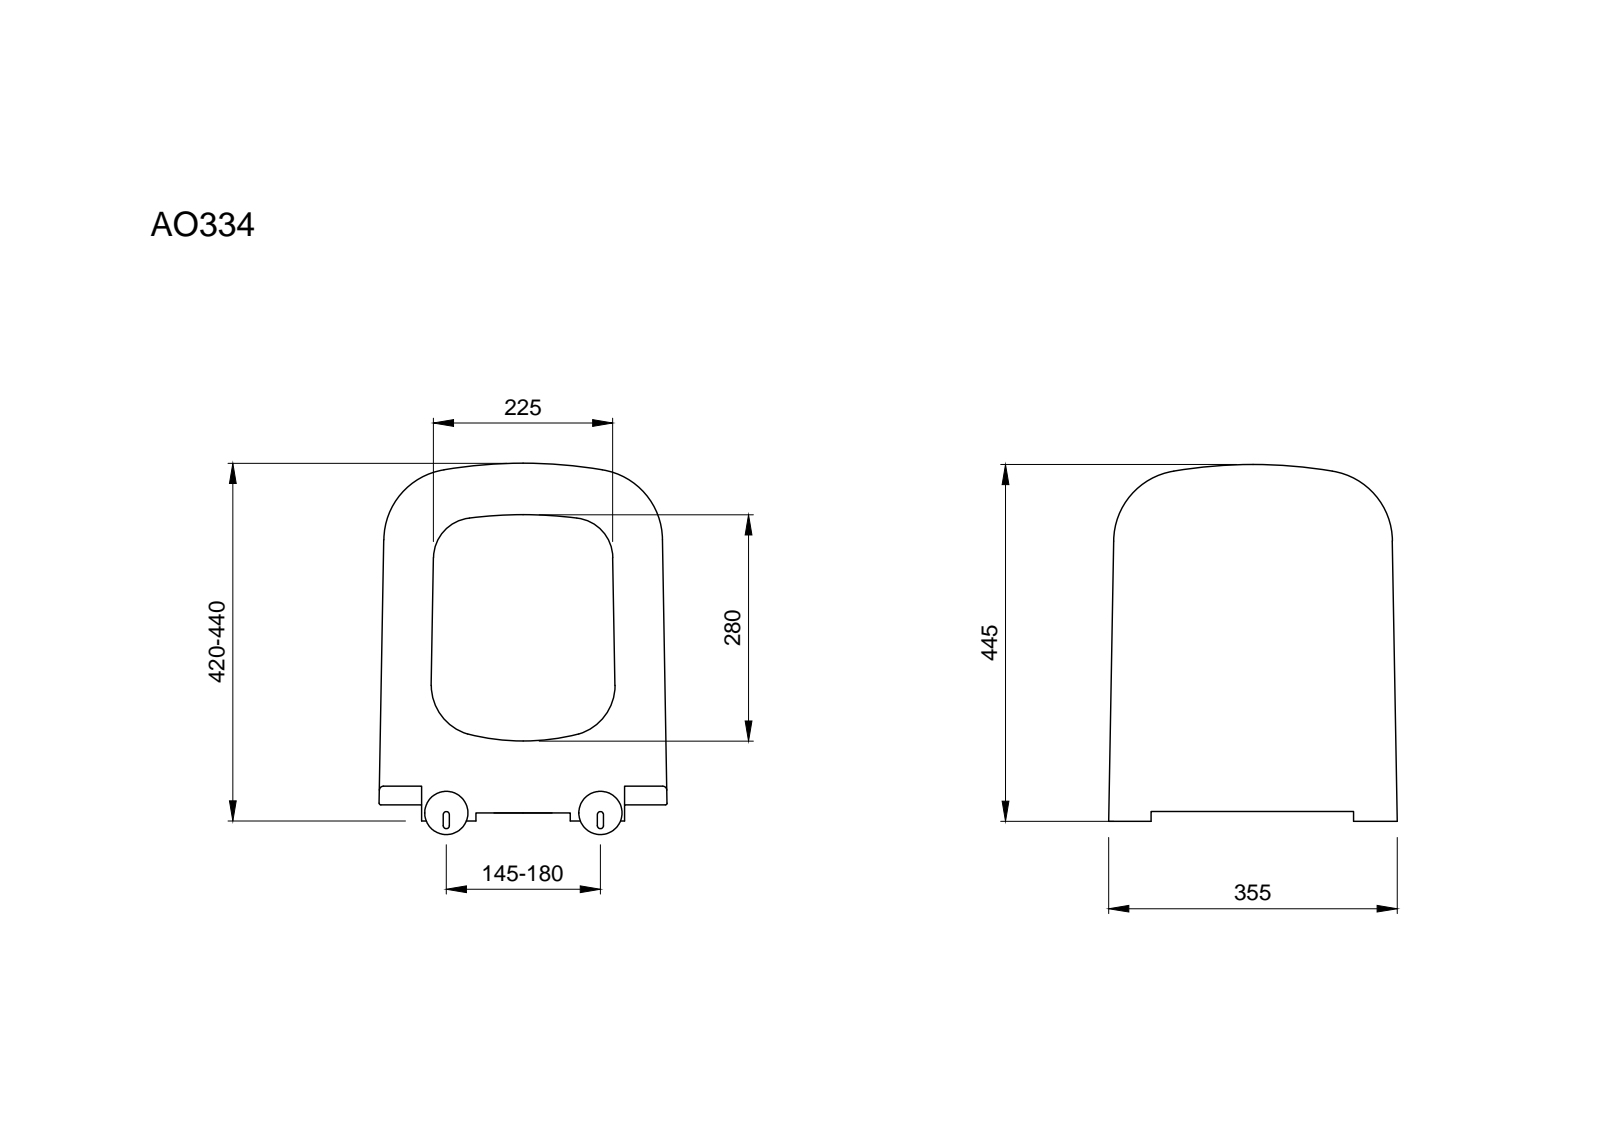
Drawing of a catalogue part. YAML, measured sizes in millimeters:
part_name: "CAN0698D77C7gtv"
step_written_by: "SIEMENS PLM Software NX 11.0 (AUTOMOTIVE_DESIGN)"
units: millimeters
bodies: {solids: 2, faces: 334, planar: 46, cylindrical: 53, other: 235}
overall_size: [445.45, 360.11, 47]
volume: 1562000
surface_area: 559780
round_holes:
  - {diameter: 19.8, count: 1}
round_bosses_or_shafts:
  - {diameter: 34, count: 1}
partial_cylinders:
  - {radius: 1, count: 10}
  - {radius: 2, count: 10}
  - {radius: 3, count: 3}
  - {radius: 5, count: 3}
  - {radius: 3.1, count: 1}
  - {radius: 10.8, count: 1}
  - {radius: 15.3, count: 1}
  - {radius: 16, count: 1}
face_to_face_distances: [11, 5, 0.65, 19, 30, 5.65, 7, 23, 12, 4.35]
